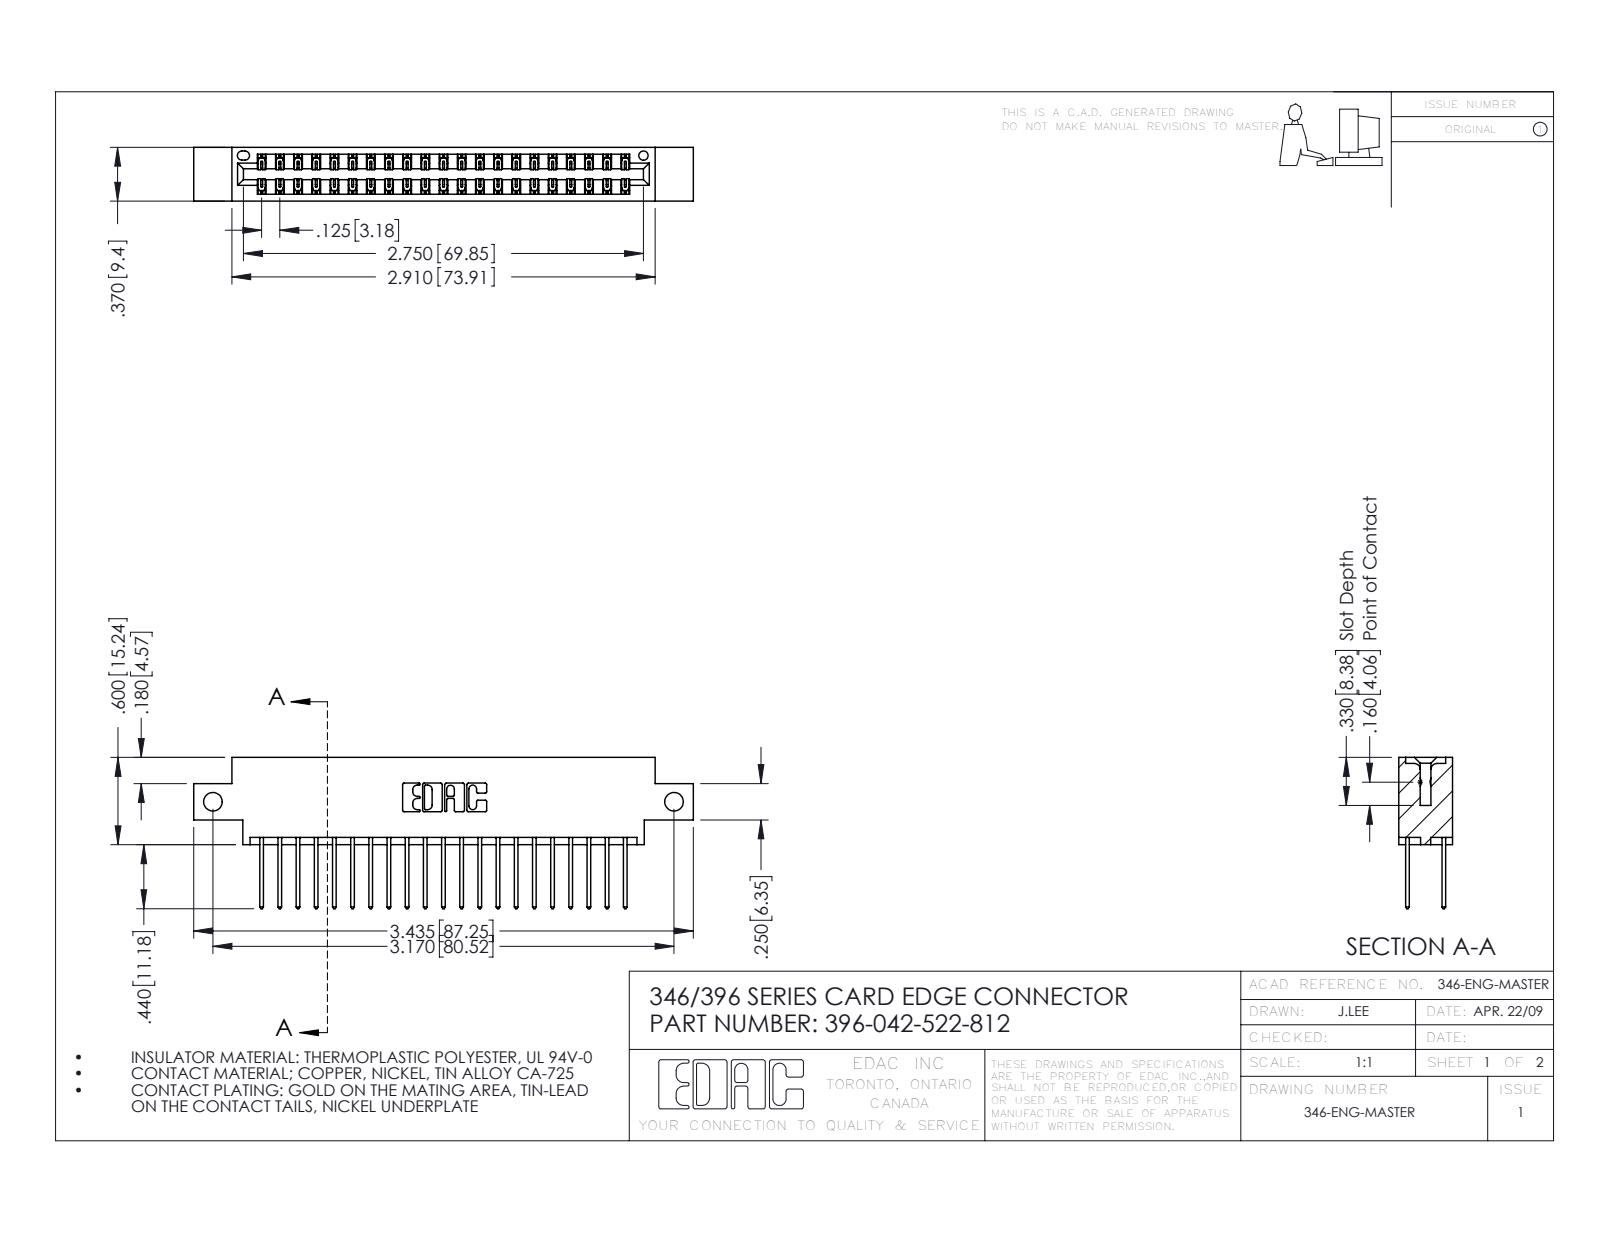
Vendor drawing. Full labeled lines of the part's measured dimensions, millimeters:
Part name (STEP PRODUCT): 345-292-001_345-293-122; 346 Part_0.170 Offset - Side Mount; 396-042-522-812
STEP written by: SolidWorks 2016 (CONFIG_CONTROL_DESIGN)
Units: millimetres
Bodies: 43 solids, 2310 faces (1550 planar, 760 cylindrical, 0 other)
Overall size (bounding box): 87.2 × 26.4 × 9.4
Volume: 8 210 mm³ · Surface area: 11 500 mm²
Round holes (diameter × count): ⌀3.3 ×2, ⌀1.6 ×1
Partial cylindrical surfaces — rounded edges, fillets, slot ends (radius × count): R0.2 ×63, R0.3 ×42, R0.3 ×22, R0.2 ×6, R0.8 ×6, R0.7 ×3, R0.4 ×2, R0.6 ×2
Main face-to-face distances: 1.2, 8.2, 6.4, 9.4, 1.8, 7.6, 0.6, 7, 3.8, 5.6
Hole centre spacings: 80.5
